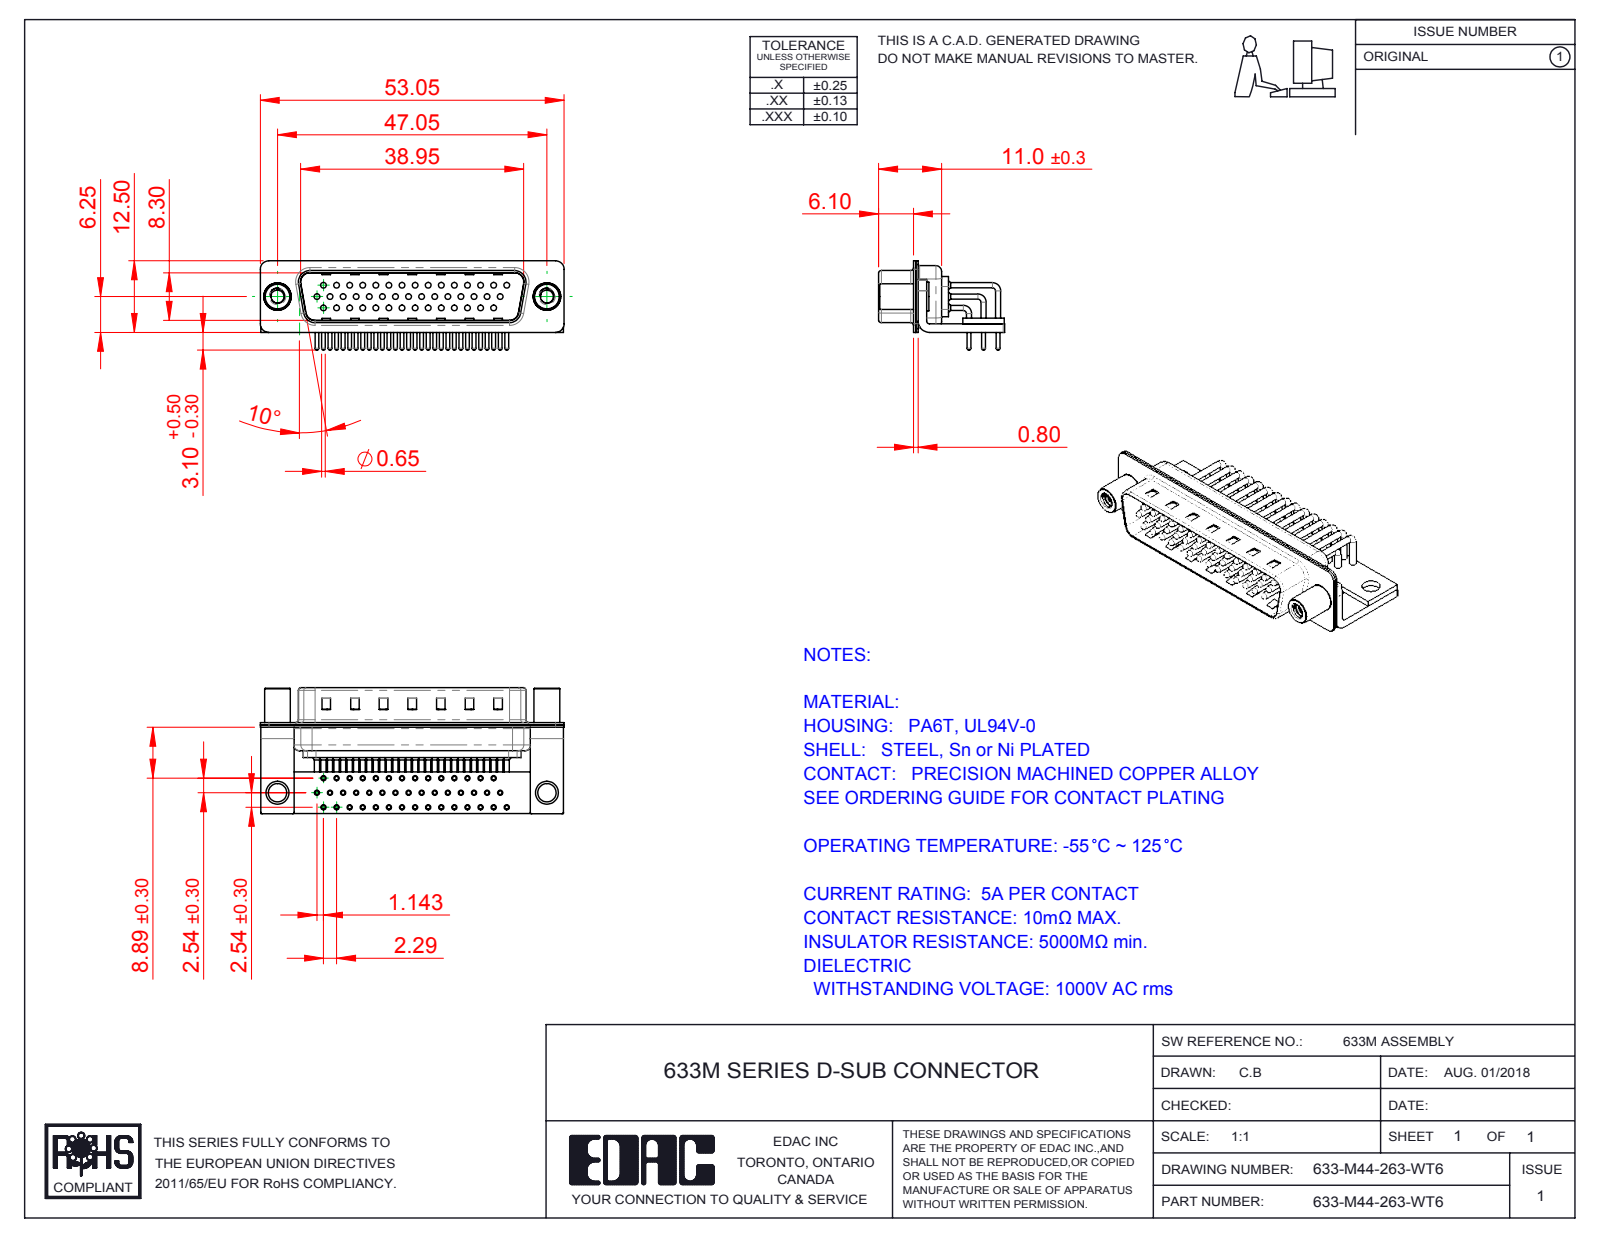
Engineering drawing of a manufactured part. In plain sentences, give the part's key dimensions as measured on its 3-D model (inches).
The part is named "633-M44-263-WT6; 633M Contact Row 2; 633M Contact Row 1; 633M Shell Rear_44 Contacts (+6 more)". Its 3-D file was written by "SolidWorks 2016 (CONFIG_CONTROL_DESIGN)". It is 52 solids with 5404 faces: 3015 planar, 1873 cylindrical and 516 other. Overall it measures 2.089 by 0.866 by 0.614 inches. Its volume is 0.237 cubic inches and its surface area 18.49 square inches. Round holes: 44 of diameter 0.035, 44 of diameter 0.039, 44 of diameter 0.067, 44 of diameter 0.079, 2 of diameter 0.089, 2 of diameter 0.126, 2 of diameter 0.157, 2 of diameter 0.189. Round bosses or shafts: 45 of diameter 0.035, 44 of diameter 0.059, 44 of diameter 0.026, 2 of diameter 0.197, 2 of diameter 0.193, 2 of diameter 0.177, 2 of diameter 0.039. Partial cylindrical surfaces (rounded edges, fillets, slot ends): 44 of radius 0.04, 16 of radius 0.01, 16 of radius 0.059, 13 of radius 0.079, 9 of radius 0.02, 8 of radius 0.063, 4 of radius 0.024, 4 of radius 0.026. The main face-to-face distances are 0.016, 0.033, 0.059, 0.049, 0.039, 0.075, 0.376, 0.031, 0.409, 0.327. The hole center spacings are 0.09, 0.09, 0.18, 0.27, 0.156, 0.45, 0.324, 0.63.
